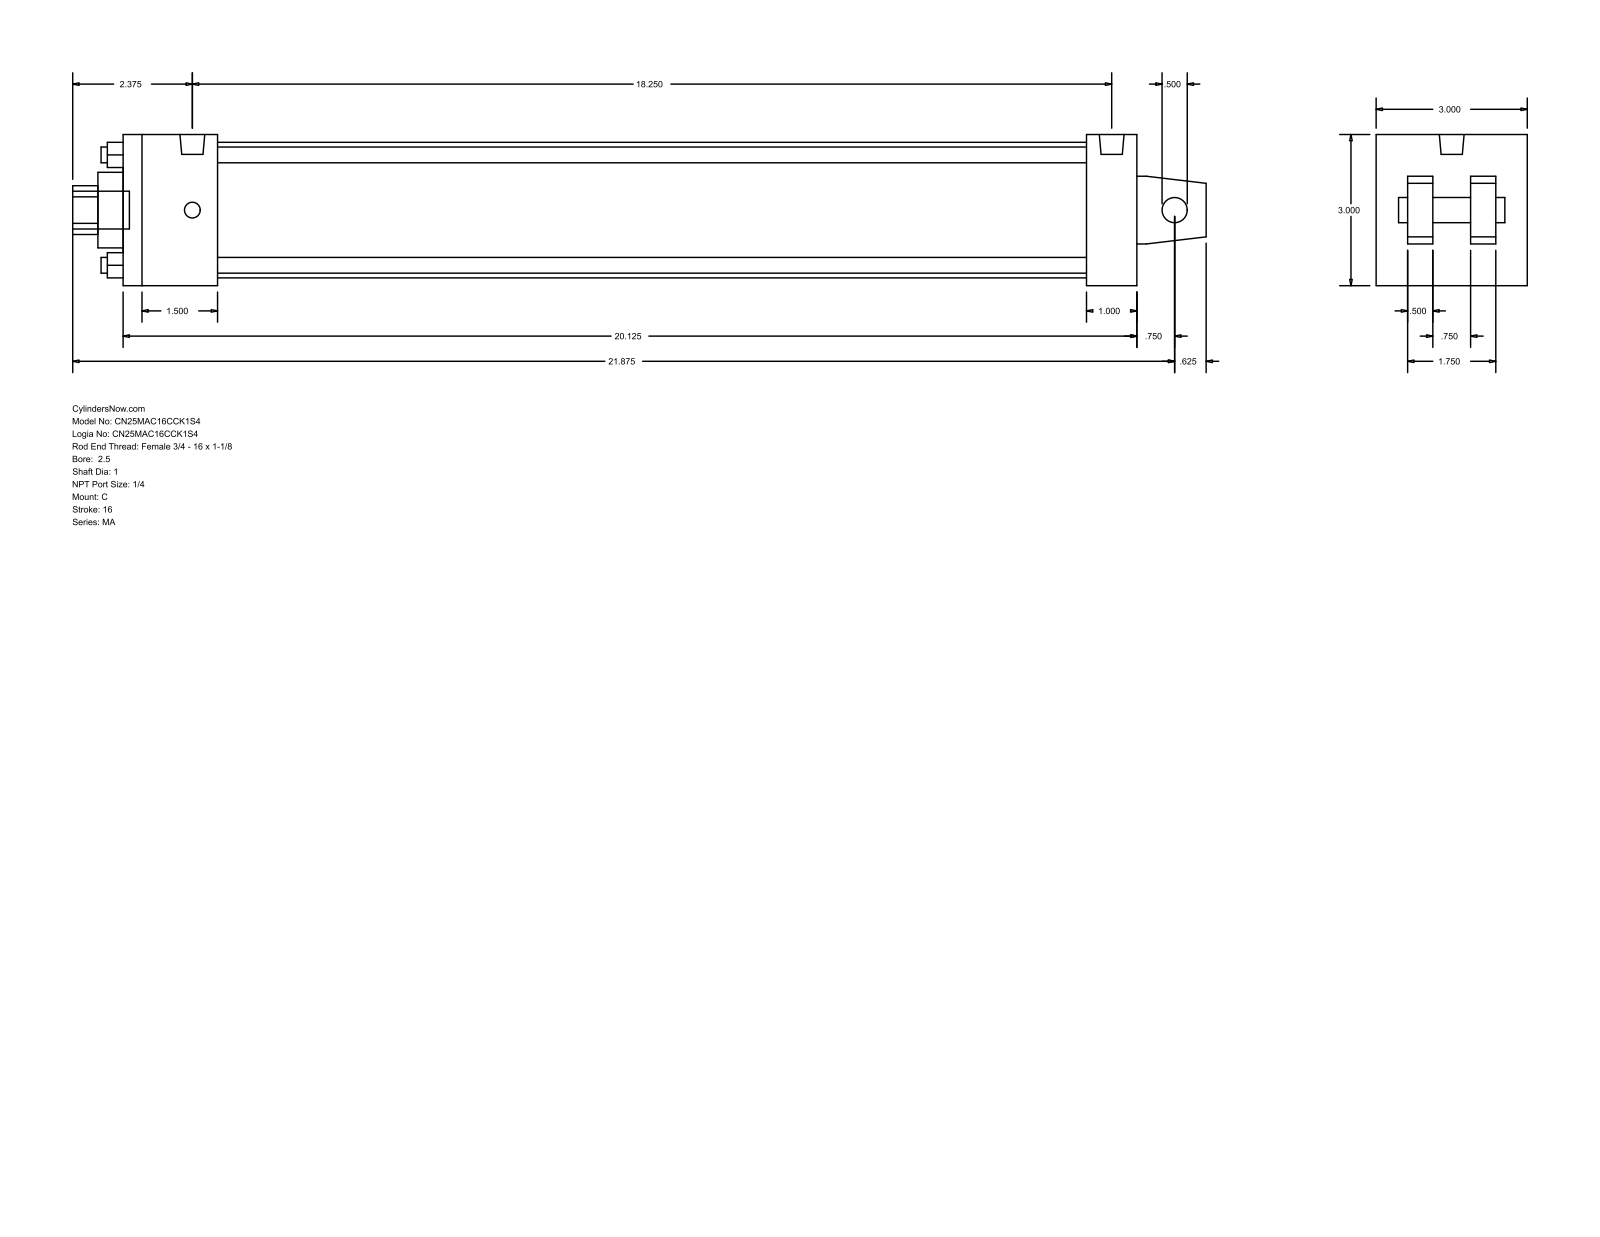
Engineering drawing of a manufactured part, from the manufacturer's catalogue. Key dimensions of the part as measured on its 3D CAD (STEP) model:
Part name (STEP PRODUCT): MA_C__0250_1
STEP written by: GSSL Pune (CONFIG_CONTROL_DESIGN)
Units: millimetres
Bodies: 0 solids, 103 faces (76 planar, 27 cylindrical, 0 other)
Overall size (bounding box): 571.5 × 76.2 × 76.2
Round holes (diameter × count): ⌀7.94 ×4, ⌀12.7 ×1, ⌀25.4 ×1, ⌀38.1 ×1, ⌀68.33 ×1
Round bosses / shafts (diameter × count): ⌀7.94 ×4, ⌀12.49 ×2, ⌀19.05 ×1
Partial cylindrical surfaces — rounded edges, fillets, slot ends (radius × count): R12.29 ×1
Main face-to-face distances: 76.2, 511.18, 47.63, 12.7, 15.87, 60.33, 25.4, 28.57, 485.78, 438.15
Hole centre spacings: 39.33, 55.62, 78.66
